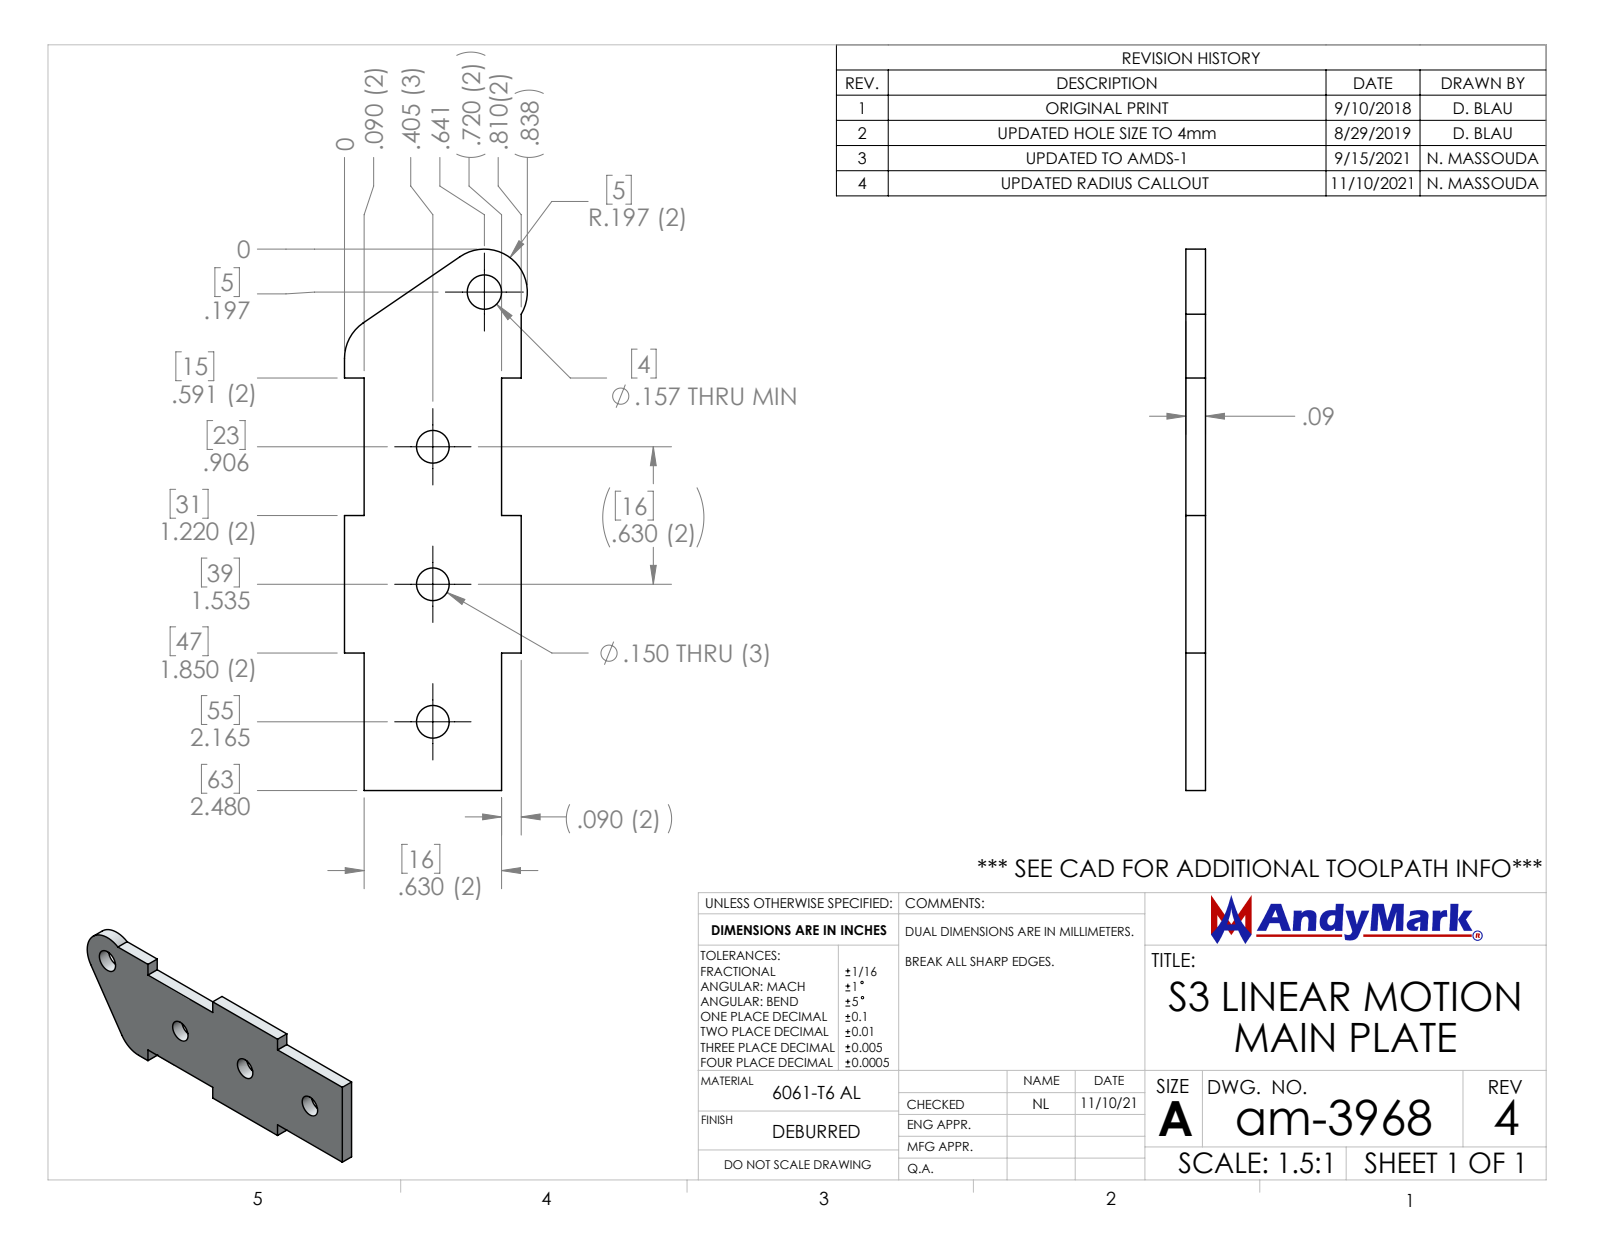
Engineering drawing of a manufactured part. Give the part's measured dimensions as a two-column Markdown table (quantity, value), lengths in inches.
| quantity | value |
| --- | --- |
| part name | am-3968 S3 Linear Motion Main Plate |
| STEP written by | SolidWorks 2021 (CONFIG_CONTROL_DESIGN) |
| units | inches |
| bodies | 1 solid, 28 faces (18 planar, 10 cylindrical, 0 other) |
| overall size | 2.48 × 0.838 × 0.09 |
| volume | 0.143 in³ |
| surface area | 3.949 in² |
| round holes (diameter × count) | 0.15 × 3, 0.157 × 1 |
| partial cylindrical surfaces (radius × count) | 0.197 × 2 |
| main face-to-face distances | 0.09, 0.63, 0.72, 0.81, 1.26, 1.89 |
| hole center spacings | 0.63, 0.747, 1.26, 1.359, 1.983 |
